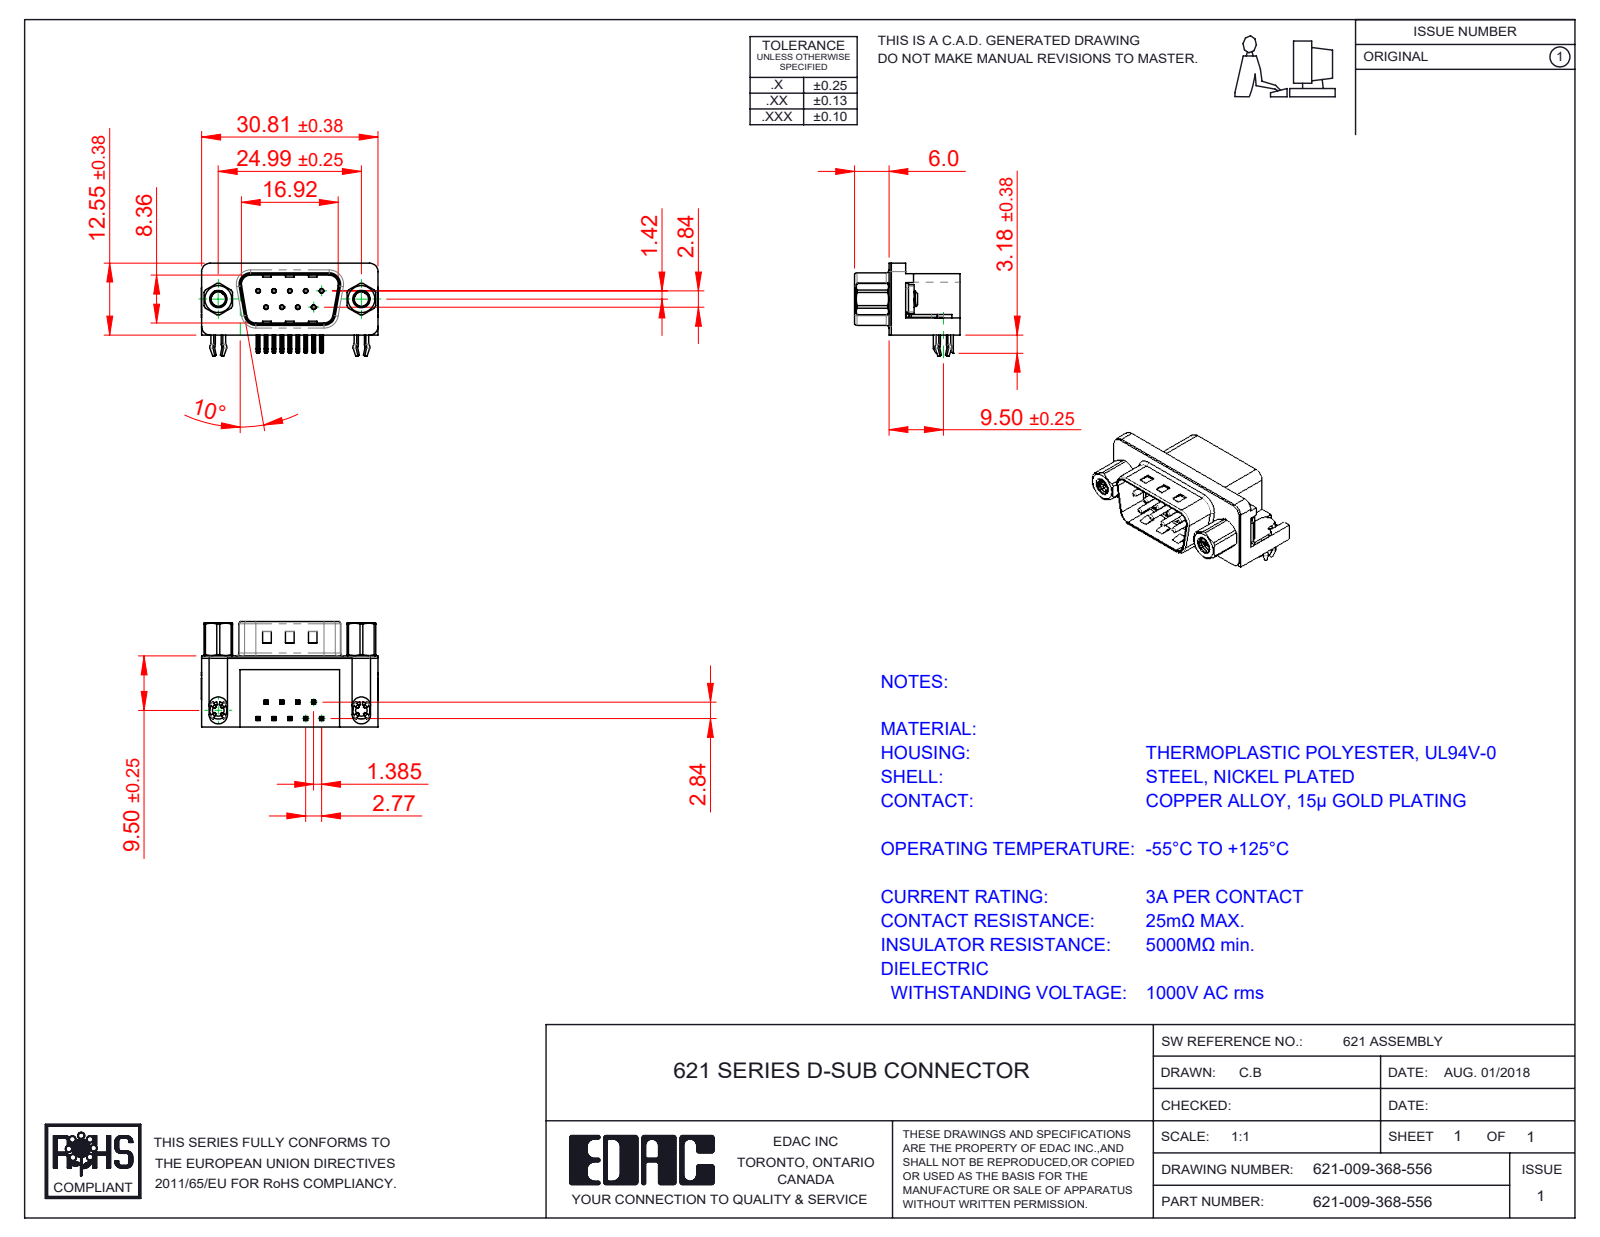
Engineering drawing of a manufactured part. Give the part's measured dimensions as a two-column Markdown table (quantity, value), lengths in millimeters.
| quantity | value |
| --- | --- |
| part name | 621-009-368-556; 621 Contact Bottom; 621 Housing_9 Socket; 621 4-40 Threaded Board Mount (+4 more) |
| STEP written by | SolidWorks 2016 (CONFIG_CONTROL_DESIGN) |
| units | millimeters |
| bodies | 17 solids, 1169 faces (595 planar, 423 cylindrical, 151 other) |
| overall size | 30.89 × 18.4 × 15.73 |
| volume | 3 497 mm³ |
| surface area | 5 032 mm² |
| round holes (diameter × count) | 0.35 × 9, 0.8 × 9, 2.26 × 2, 2.5 × 2, 4 × 2, 4.8 × 2, 5 × 2 |
| round bosses / shafts (diameter × count) | 0.75 × 9, 4.9 × 2, 4.75 × 2, 3.9 × 2, 3.26 × 2, 3 × 2 |
| partial cylindrical surfaces (radius × count) | 0.25 × 44, 0.12 × 18, 1 × 16, 0.5 × 9, 1.5 × 8, 1.6 × 8, 0.9 × 4, 2 × 4 |
| main face-to-face distances | 0.4, 12, 12.4, 10.35, 9.5, 2.5, 2.9, 0.5, 2.1, 0.35 |
| hole center spacings | 3.16, 2.77, 5.54, 5.03, 5.04, 8.31, 7.48, 7.49 |
